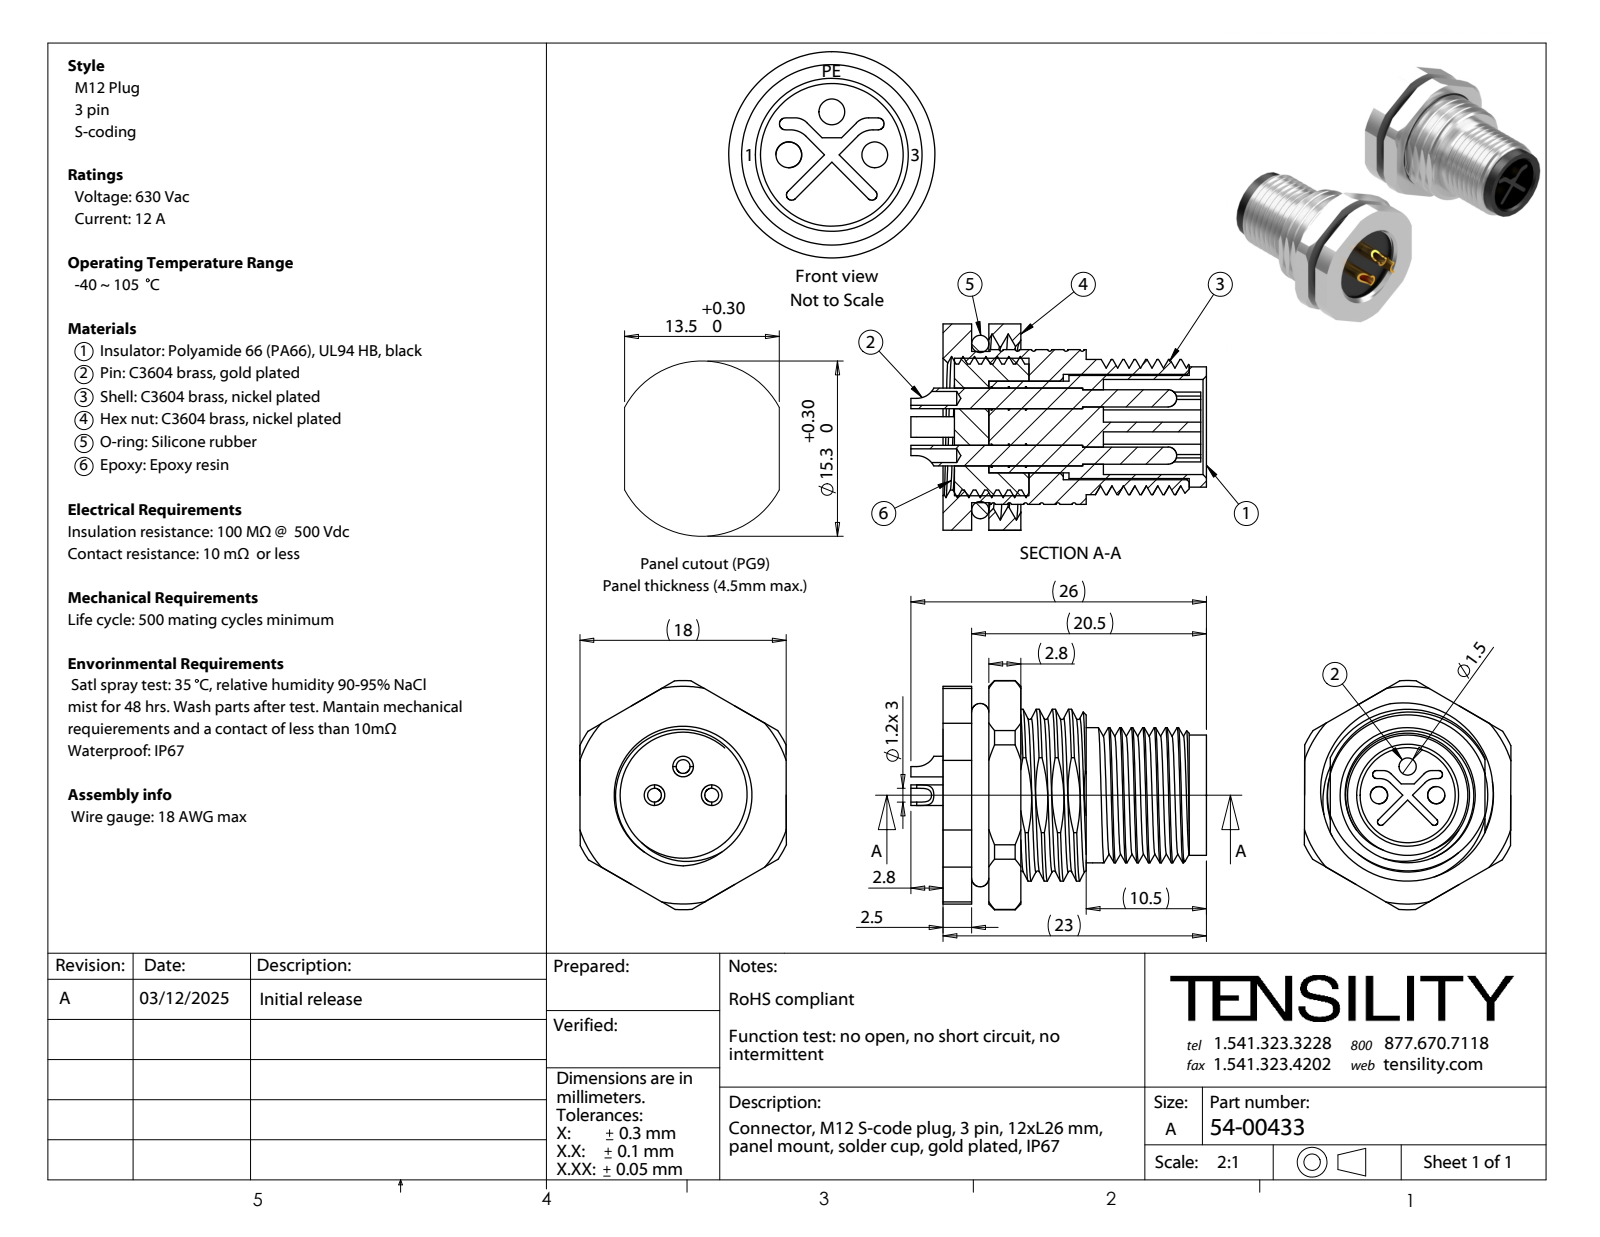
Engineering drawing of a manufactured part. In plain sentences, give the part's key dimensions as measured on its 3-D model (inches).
The part is named "54-00433-05; 54-00433-01; 54-00433; 54-00433-04 (+3 more)". Its 3-D file was written by "SolidWorks 2021 (CONFIG_CONTROL_DESIGN)". It is 8 solids with 311 faces: 84 planar, 143 cylindrical and 84 other. Overall it measures 1.016 by 0.787 by 0.71 inches. Its volume is 0.19 cubic inches and its surface area 9.013 square inches. Round holes: 3 of diameter 0.047, 3 of diameter 0.059, 1 of diameter 0.315, 1 of diameter 0.327, 1 of diameter 0.362, 1 of diameter 0.433, 1 of diameter 0.551. Round bosses or shafts: 3 of diameter 0.071, 1 of diameter 0.52, 1 of diameter 0.472, 1 of diameter 0.465, 1 of diameter 0.413, 1 of diameter 0.354. Partial cylindrical surfaces (rounded edges, fillets, slot ends): 3 of radius 0.067, 2 of radius 0.012, 2 of radius 0.014, 2 of radius 0.039, 2 of radius 0.05, 1 of radius 0.295, 1 of radius 0.374, 1 of radius 0.394. The main face-to-face distances are 0.059, 0.157, 0.256, 0.197, 0.295, 0.098, 0.138, 0.118, 0.709, 0.039. The hole center spacings are 0.098, 0.139, 0.197.
